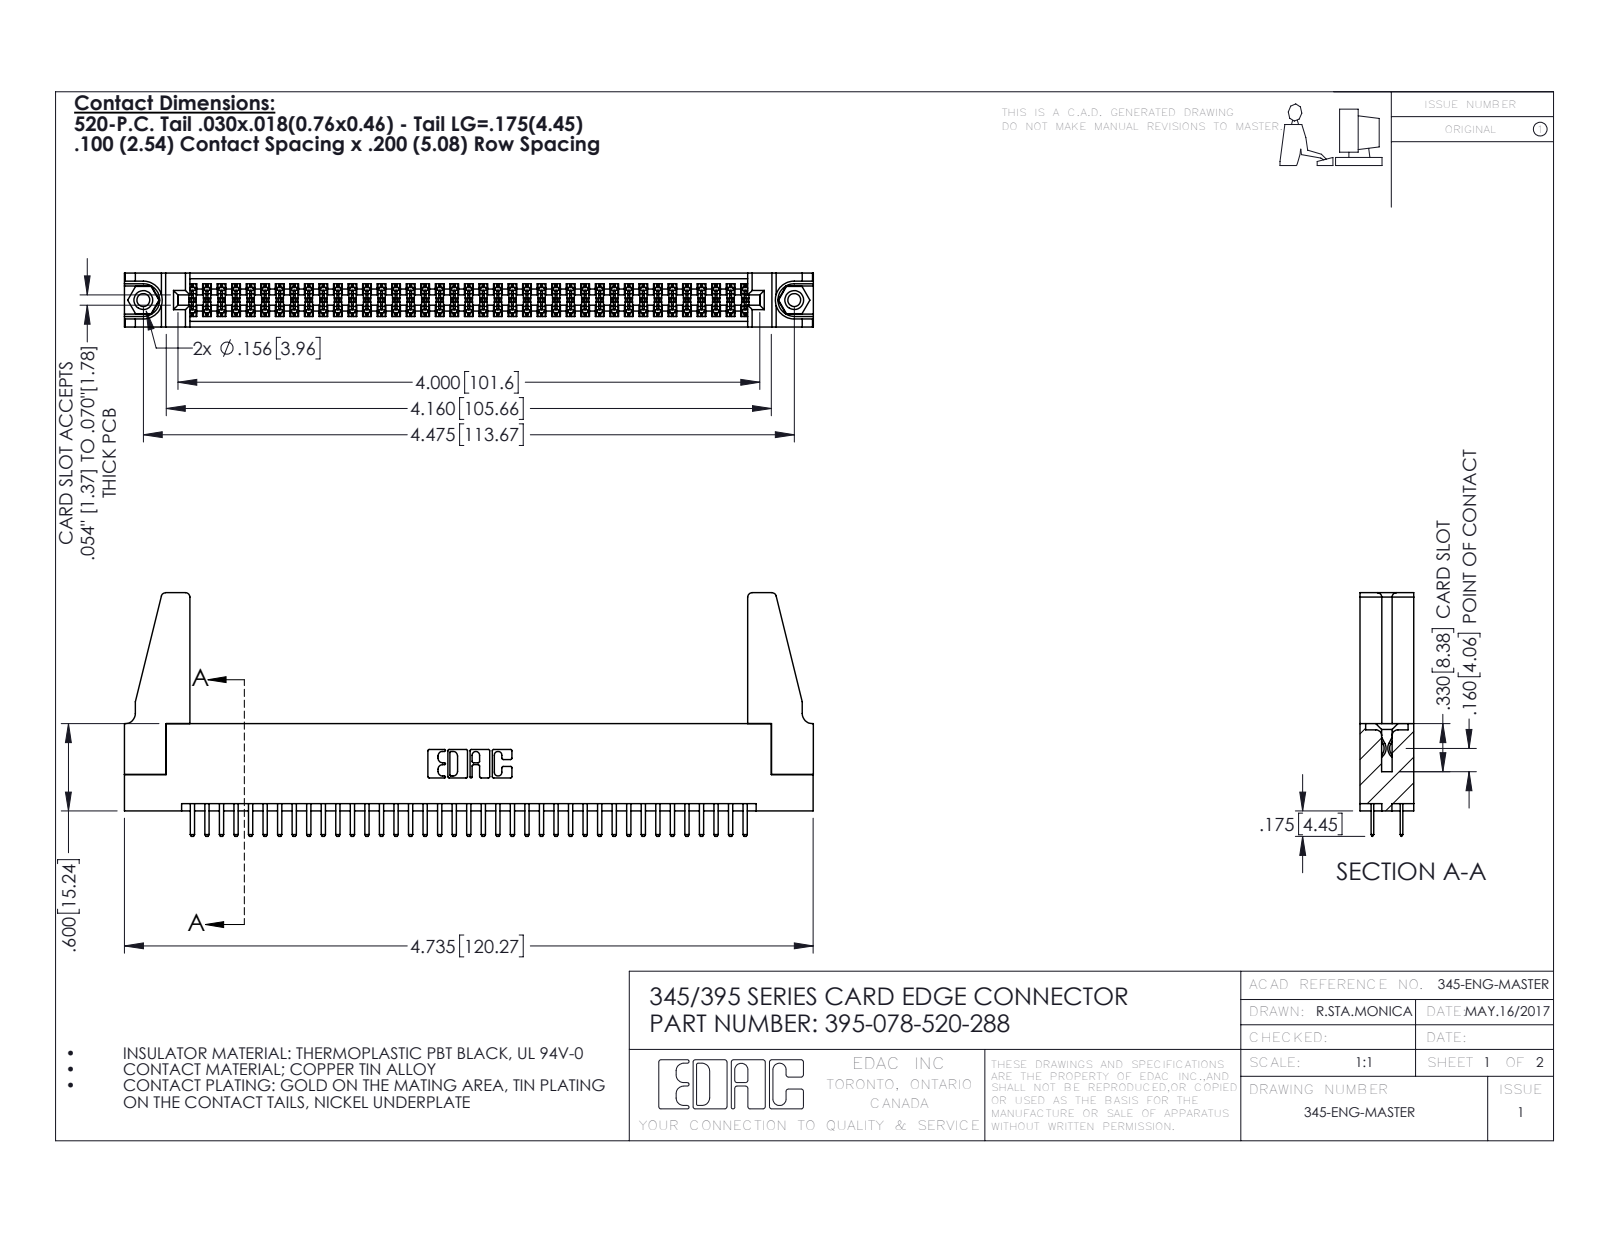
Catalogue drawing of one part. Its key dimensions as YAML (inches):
part_name: "345-250-001_345-250-001-102; 345 Part_Flush Mounting Lugs - 0.156 Dia-TH; 395-078-520-288; 345-220-078_345-220-088 (+1 more)"
step_written_by: "SolidWorks 2016 (CONFIG_CONTROL_DESIGN)"
units: inches
bodies: {solids: 83, faces: 4462, planar: 2882, cylindrical: 1564, other: 16}
overall_size: [4.736, 1.675, 0.37]
volume: 0.908
surface_area: 31.27
round_holes:
  - {diameter: 0.089, count: 2}
  - {diameter: 0.125, count: 2}
  - {diameter: 0.156, count: 2}
  - {diameter: 0.064, count: 1}
round_bosses_or_shafts:
  - {diameter: 0.155, count: 2}
partial_cylinders:
  - {radius: 0.006, count: 117}
  - {radius: 0.01, count: 82}
  - {radius: 0.01, count: 22}
  - {radius: 0.03, count: 8}
  - {radius: 0.007, count: 6}
  - {radius: 0.031, count: 6}
  - {radius: 0.026, count: 3}
  - {radius: 0.014, count: 2}
face_to_face_distances: [0.072, 0.298, 0.37, 0.2, 0.098, 0.272, 0.025, 0.225, 0.022, 0.072]
hole_center_spacings: [0.27, 4.239, 4.475]
